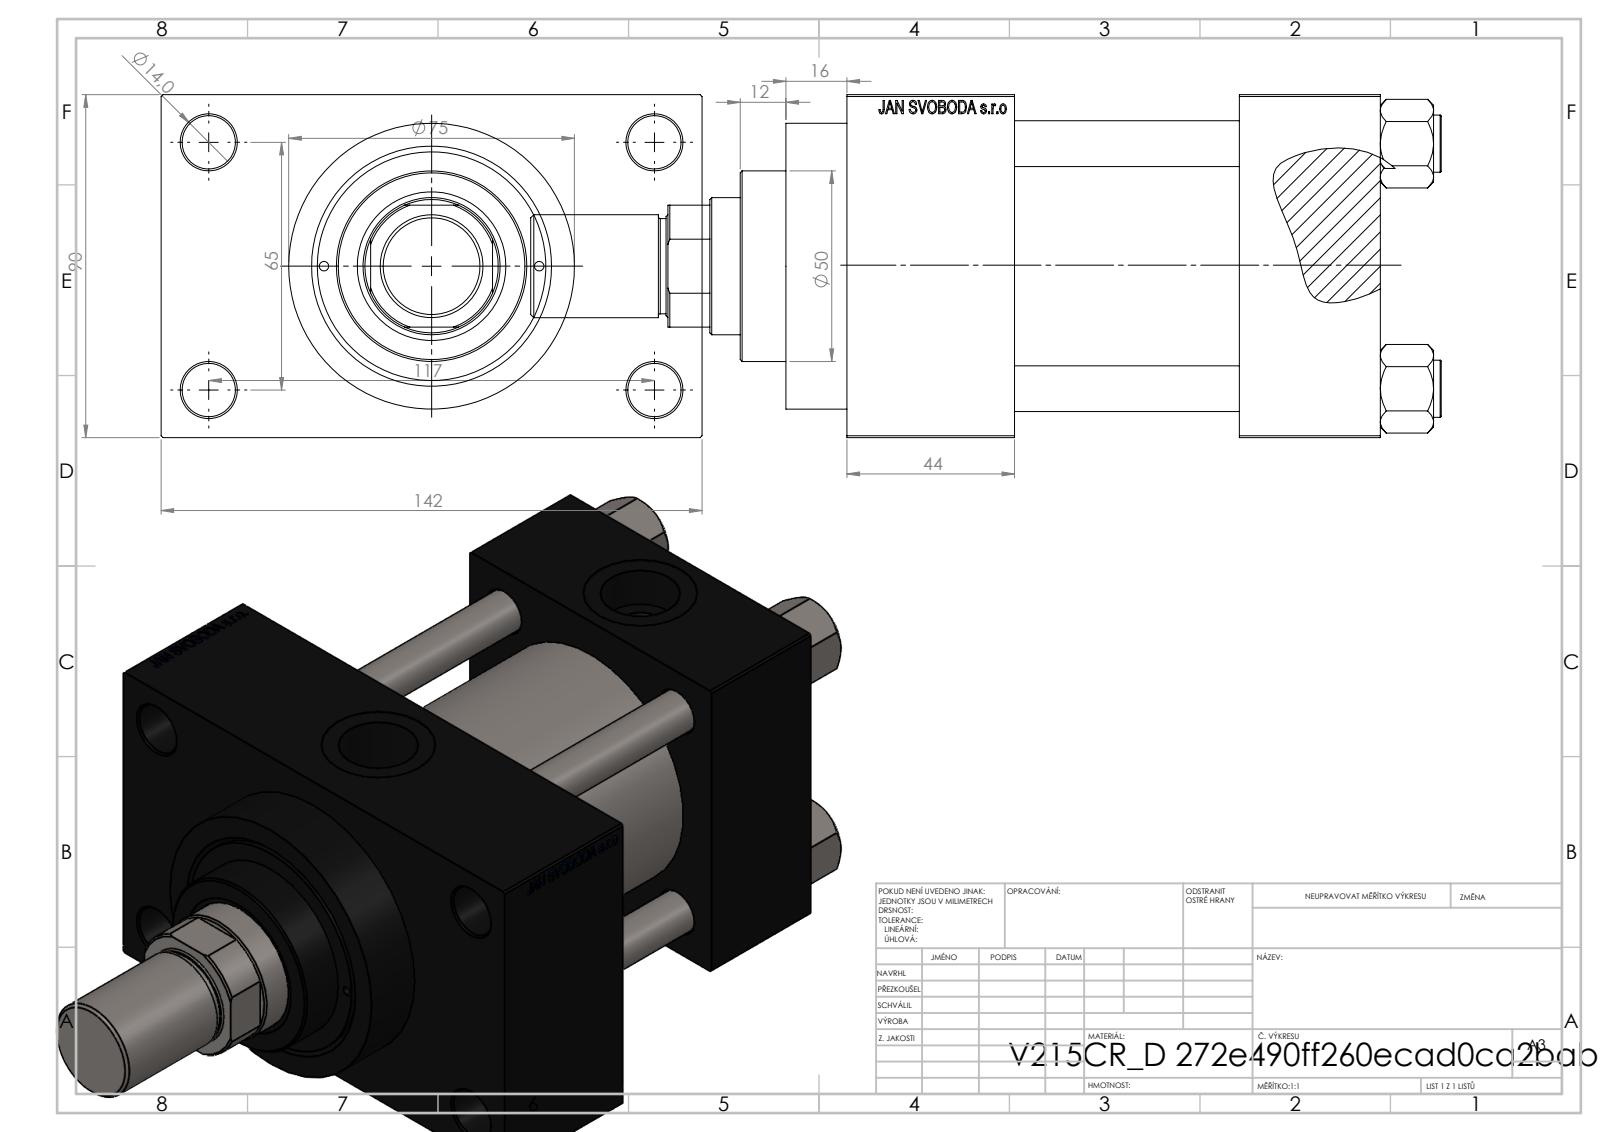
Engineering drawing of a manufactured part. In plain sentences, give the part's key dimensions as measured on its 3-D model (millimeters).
The part is named "NUT_M5_D; V215CR_D_TYCINKA; V215CR_D_Body; V215CR_VCP_D (+2 more)". Its 3-D file was written by "SolidWorks 2019 (CONFIG_CONTROL_DESIGN)". It is 12 solids with 1126 faces: 503 planar, 97 cylindrical and 526 other. Overall it measures 239 by 142 by 90 millimeters. Its volume is 1 141 000 cubic millimeters and its surface area 208 260 square millimeters. Round holes: 4 of diameter 12, 4 of diameter 14, 2 of diameter 2.5, 2 of diameter 7, 2 of diameter 20.96, 2 of diameter 30, 1 of diameter 25.5, 1 of diameter 36, 1 of diameter 39, 1 of diameter 50, 1 of diameter 60, 1 of diameter 63. Round bosses or shafts: 4 of diameter 15, 1 of diameter 75, 1 of diameter 69, 1 of diameter 27, 1 of diameter 25. Partial cylindrical surfaces (rounded edges, fillets, slot ends): 1 of radius 17.5. The main face-to-face distances are 90, 59, 37, 96, 140, 103, 44, 26, 116, 142. The hole center spacings are 26.35, 32.39, 44.4, 45.47, 64.3, 66.92, 68.42, 69.81.
